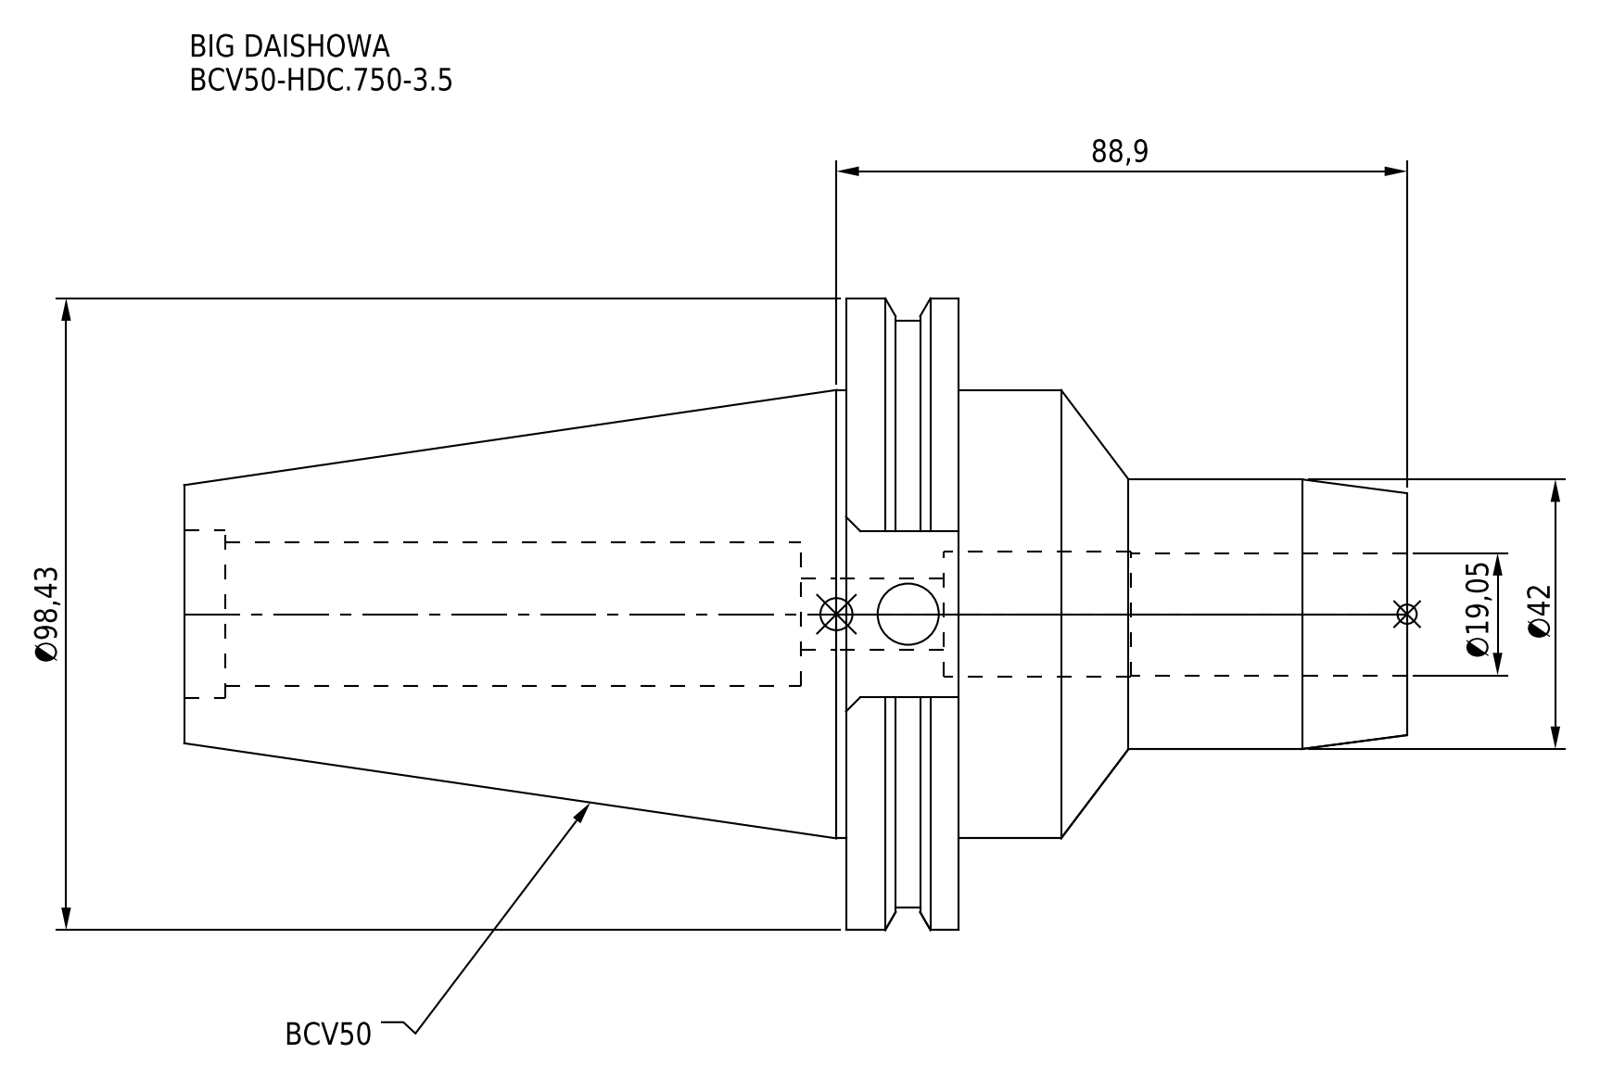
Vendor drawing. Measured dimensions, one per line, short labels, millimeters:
name: BCV50-HDC_750-3_5
written by: CREO PARAMETRIC BY PTC INC, 2016380 (AUTOMOTIVE_DESIGN)
unit: mm
bodies: 1 solid, 59 faces (23 planar, 26 cylindrical, 10 other)
size: 190.5 × 98.42 × 94.95
volume: 454 821 mm³; area: 57 865 mm²
holes: 1× ⌀9.53, 1× ⌀11, 1× ⌀19.05, 1× ⌀19.6, 1× ⌀22.3, 1× ⌀26.23
bosses: 1× ⌀98.42, 1× ⌀91.29, 1× ⌀69.85, 1× ⌀42
face distances: 17.55, 69.85, 87.4, 190.5, 120.65, 103.1, 72.95, 25.92, 94.5, 24.65
